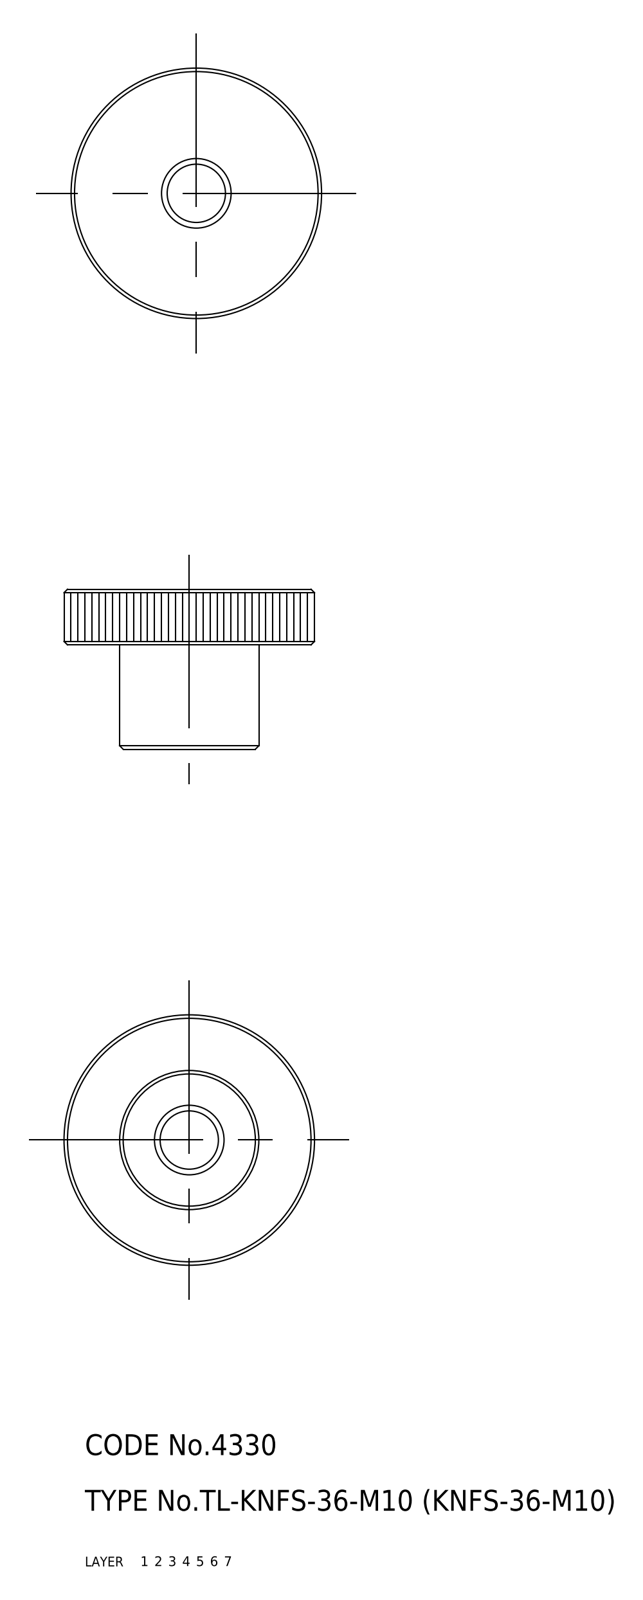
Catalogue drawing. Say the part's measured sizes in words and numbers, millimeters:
The part is named "knob". Its 3-D file was written by "CADfix (AUTOMOTIVE_DESIGN)". It is 1 solid with 15 faces: 0 planar, 0 cylindrical and 15 other. Overall it measures 36 by 36 by 23 millimeters. Its volume is 11 031 cubic millimeters and its surface area 4 365 square millimeters.
